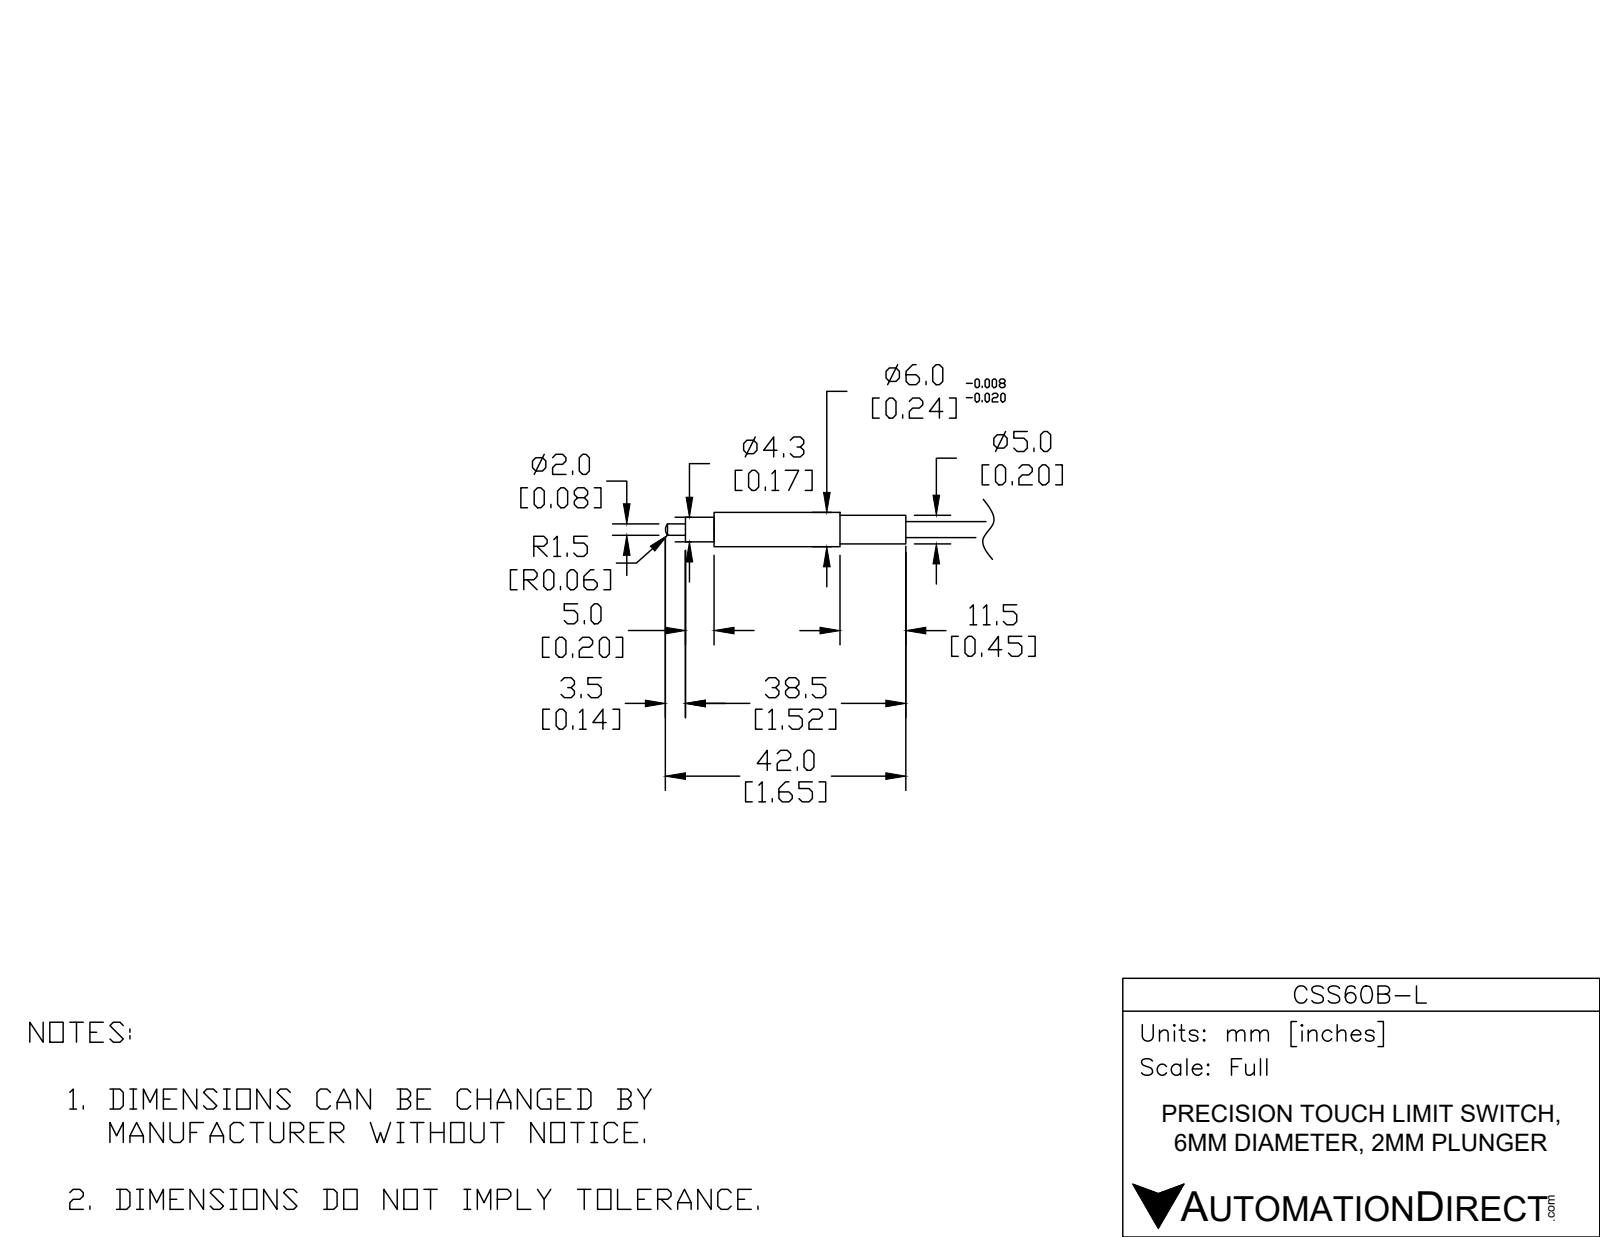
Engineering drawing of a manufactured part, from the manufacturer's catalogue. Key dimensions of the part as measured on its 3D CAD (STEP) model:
STEP written by: Spatial InterOp 3D (CONFIG_CONTROL_DESIGN)
Units: millimetres
Bodies: 1 solid, 17 faces (5 planar, 10 cylindrical, 2 other)
Overall size (bounding box): 48 × 6 × 6
Volume: 968 mm³ · Surface area: 792 mm²
Round bosses / shafts (diameter × count): ⌀6 ×1, ⌀5 ×1, ⌀4.3 ×1, ⌀2.8 ×1, ⌀2 ×1
Main face-to-face distances: 33.5, 5, 38.5, 27, 22, 11.5, 44.5, 39.5, 17.5, 6
